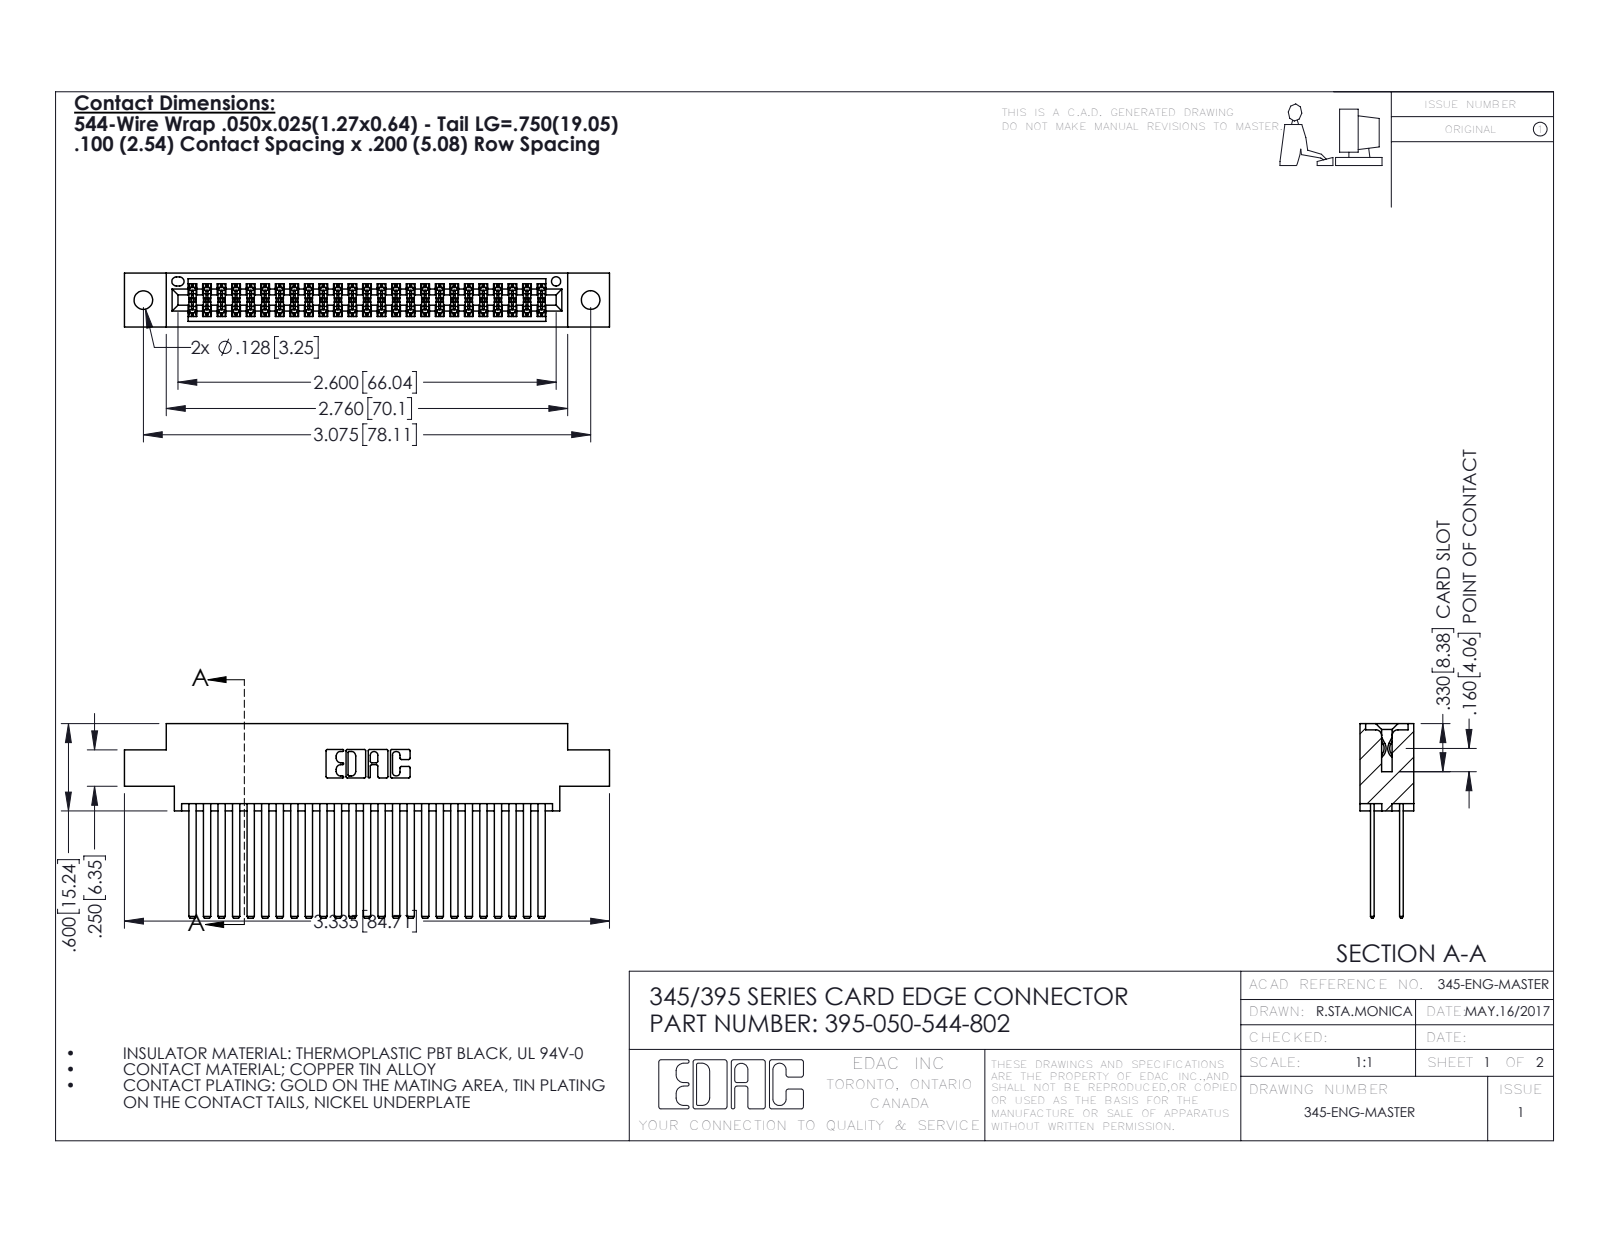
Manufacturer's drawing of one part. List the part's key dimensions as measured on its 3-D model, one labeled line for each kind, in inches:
Part name (STEP PRODUCT): 345-292-001_345-293-144; 395-050-544-802; 345 Part_0.170 Offset - 0.128 Dia
STEP written by: SolidWorks 2016 (CONFIG_CONTROL_DESIGN)
Units: inches
Bodies: 51 solids, 2330 faces (1534 planar, 796 cylindrical, 0 other)
Overall size (bounding box): 3.335 × 1.337 × 0.37
Volume: 0.526 in³ · Surface area: 22.23 in²
Round holes (diameter × count): ⌀0.128 ×2, ⌀0.064 ×1
Partial cylindrical surfaces — rounded edges, fillets, slot ends (radius × count): R0.006 ×75, R0.01 ×22, R0.007 ×6, R0.031 ×6, R0.026 ×3, R0.014 ×2, R0.019 ×2, R0.022 ×2
Main face-to-face distances: 0.2, 0.298, 0.072, 0.025, 0.098, 0.272, 0.225, 0.37, 0.175, 0.15
Hole centre spacings: 0.27, 2.84, 3.075
